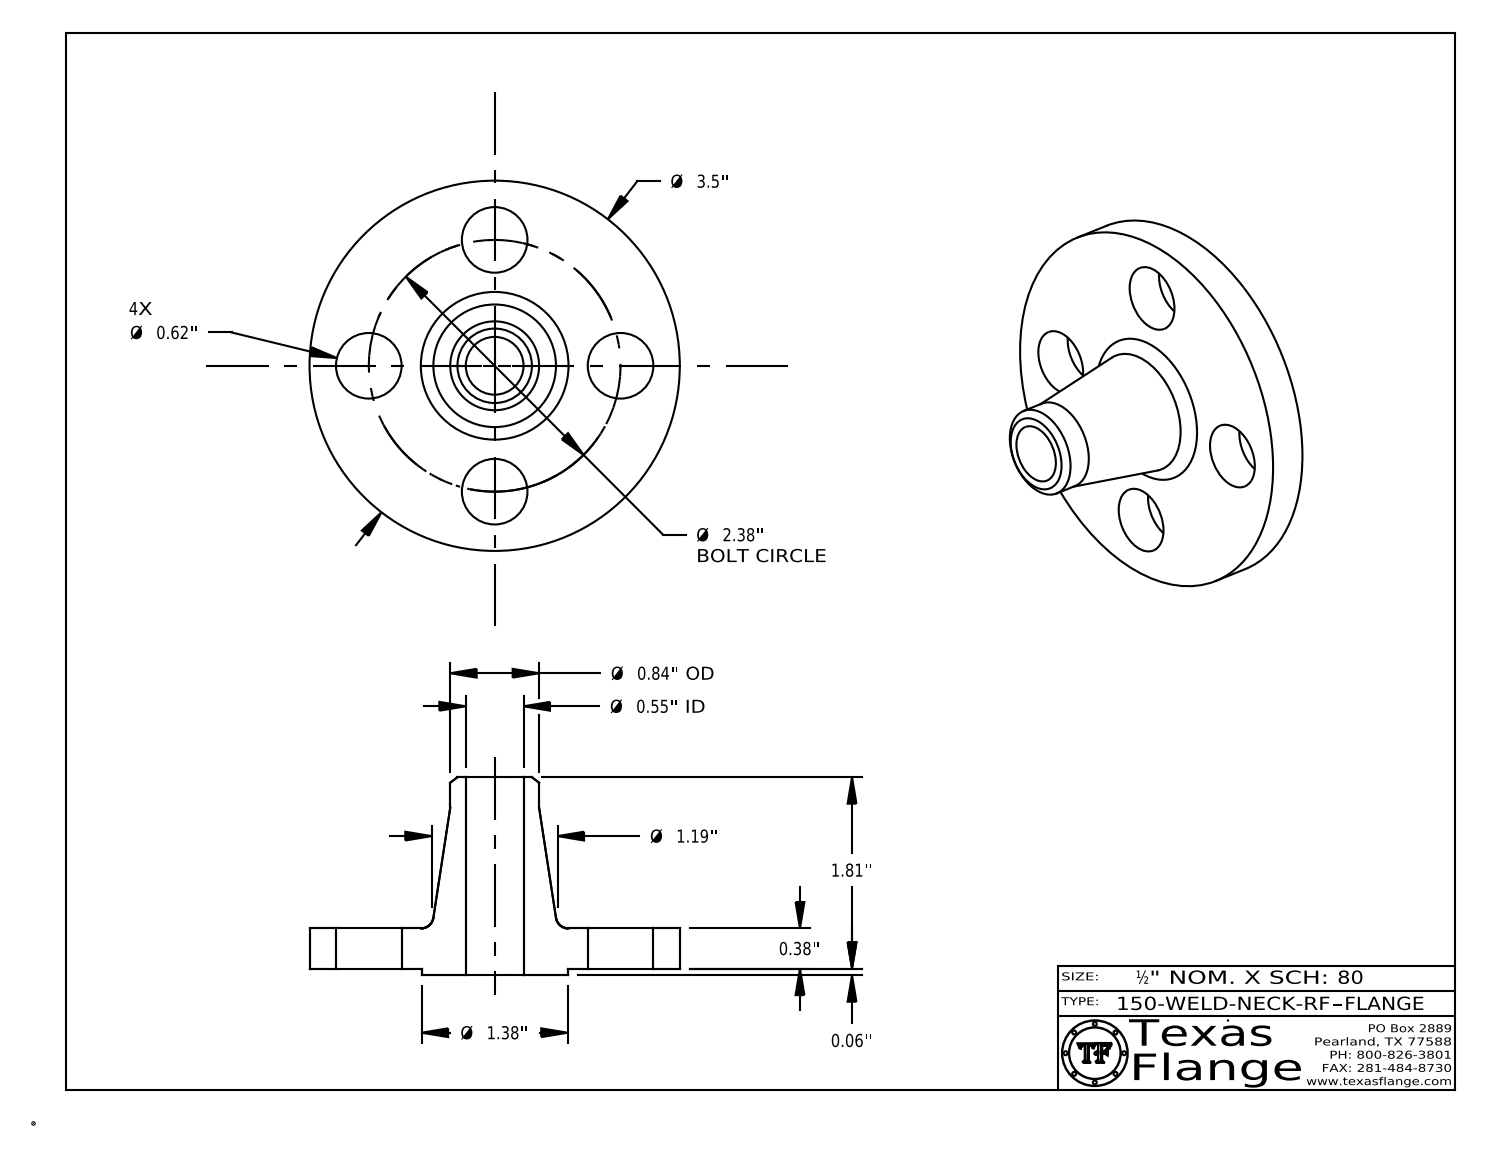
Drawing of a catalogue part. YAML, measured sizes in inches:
part_name: "150-WELD-NECK-RF"
step_written_by: "CATIA V5 STEP AP214 (AUTOMOTIVE_DESIGN)"
units: inches
bodies: {solids: 1, faces: 411, planar: 369, cylindrical: 36, other: 6}
overall_size: [3.5, 3.5, 1.873]
volume: 3.947
surface_area: 30.74
round_holes:
  - {diameter: 0.62, count: 4}
  - {diameter: 0.495, count: 1}
  - {diameter: 0.546, count: 1}
round_bosses_or_shafts:
  - {diameter: 0.03, count: 8}
  - {diameter: 3.5, count: 1}
  - {diameter: 1.38, count: 1}
  - {diameter: 0.84, count: 1}
  - {diameter: 0.39, count: 1}
face_to_face_distances: [0.38, 0.063, 0.443, 1.872, 1.81, 1.43, 0.428, 0.365, 0.015, 1.445]
hole_center_spacings: [1.19, 1.683, 0.911, 2.199, 2.38, 1.19]
